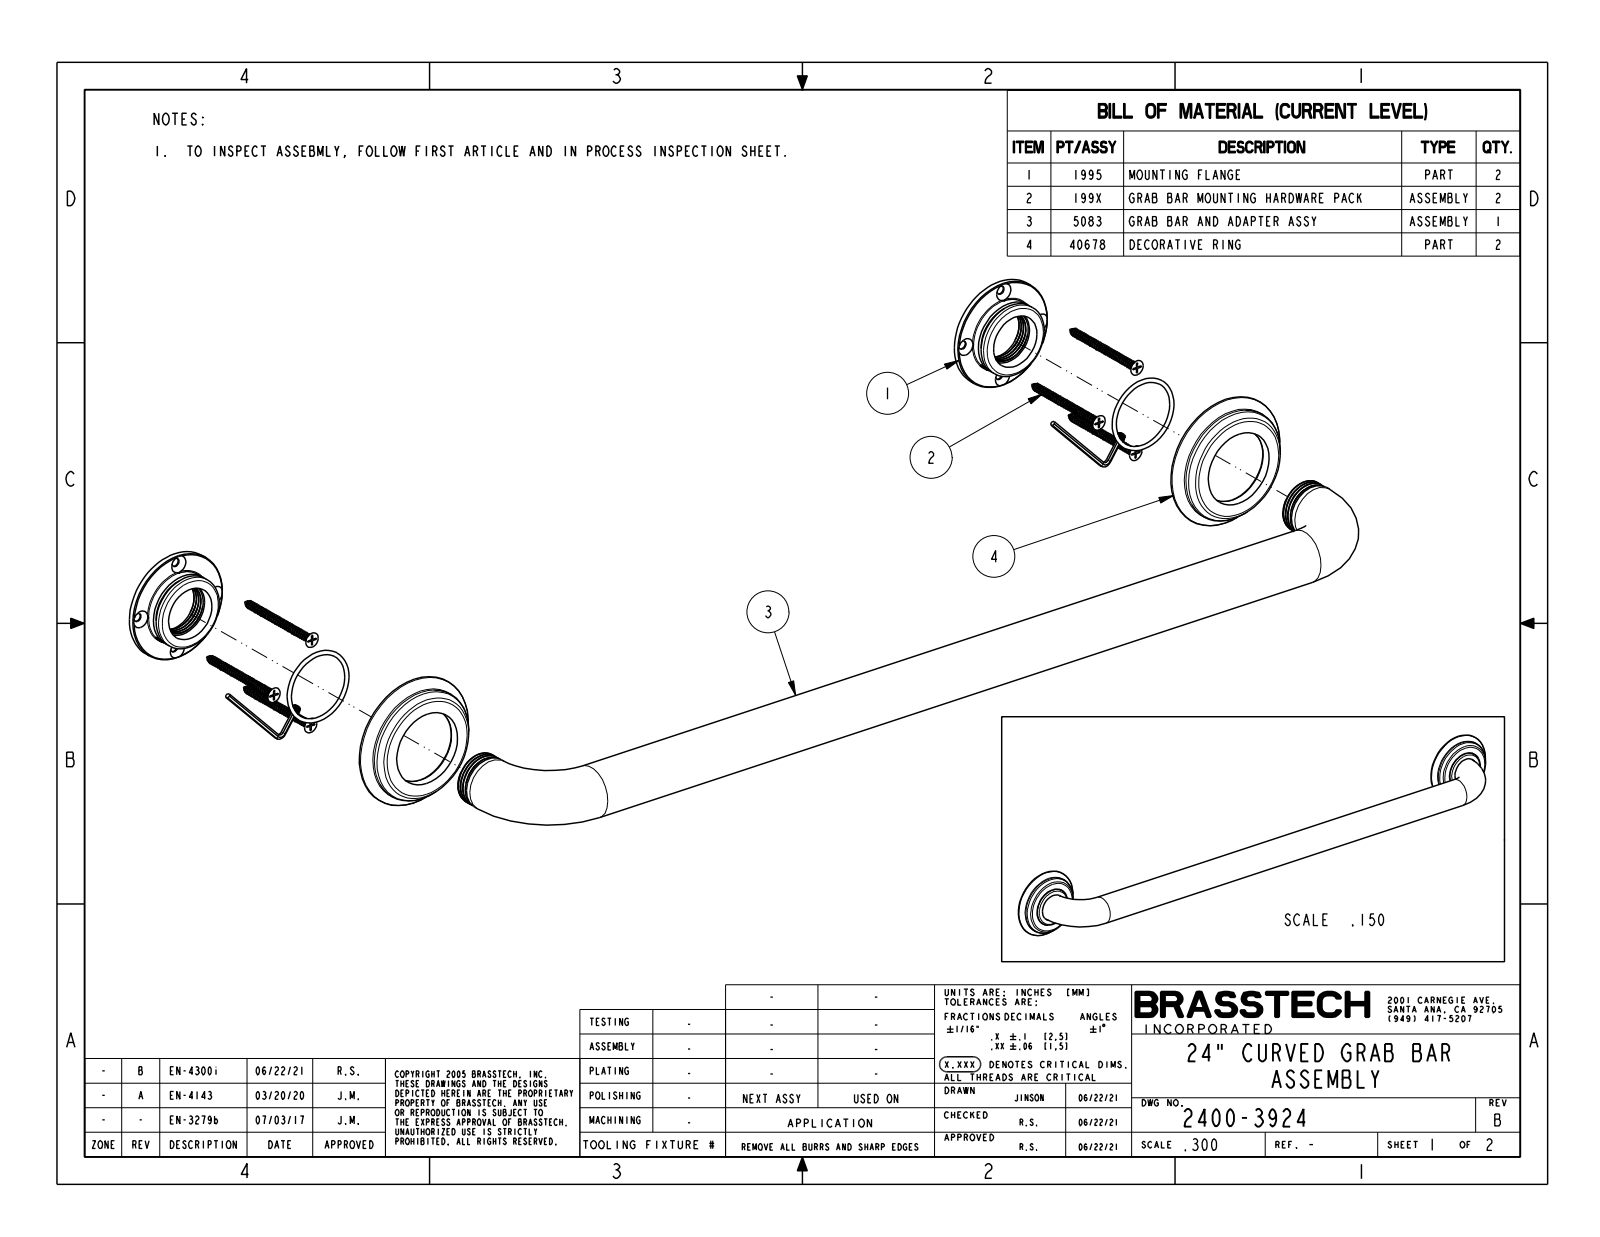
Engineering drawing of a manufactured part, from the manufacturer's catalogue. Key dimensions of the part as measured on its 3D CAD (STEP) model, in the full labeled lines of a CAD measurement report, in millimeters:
Part name (STEP PRODUCT): 2400-3924
STEP written by: CREO PARAMETRIC BY PTC INC, 2018400 (CONFIG_CONTROL_DESIGN)
Units: millimetres
Bodies: 1 solid, 44 faces (6 planar, 6 cylindrical, 32 other)
Overall size (bounding box): 689.7 × 80.1 × 69.9
Volume: 626 300 mm³ · Surface area: 87 100 mm²
Round bosses / shafts (diameter × count): ⌀44.5 ×2, ⌀31.8 ×1
Main face-to-face distances: 13.3, 15.2, 1.9
